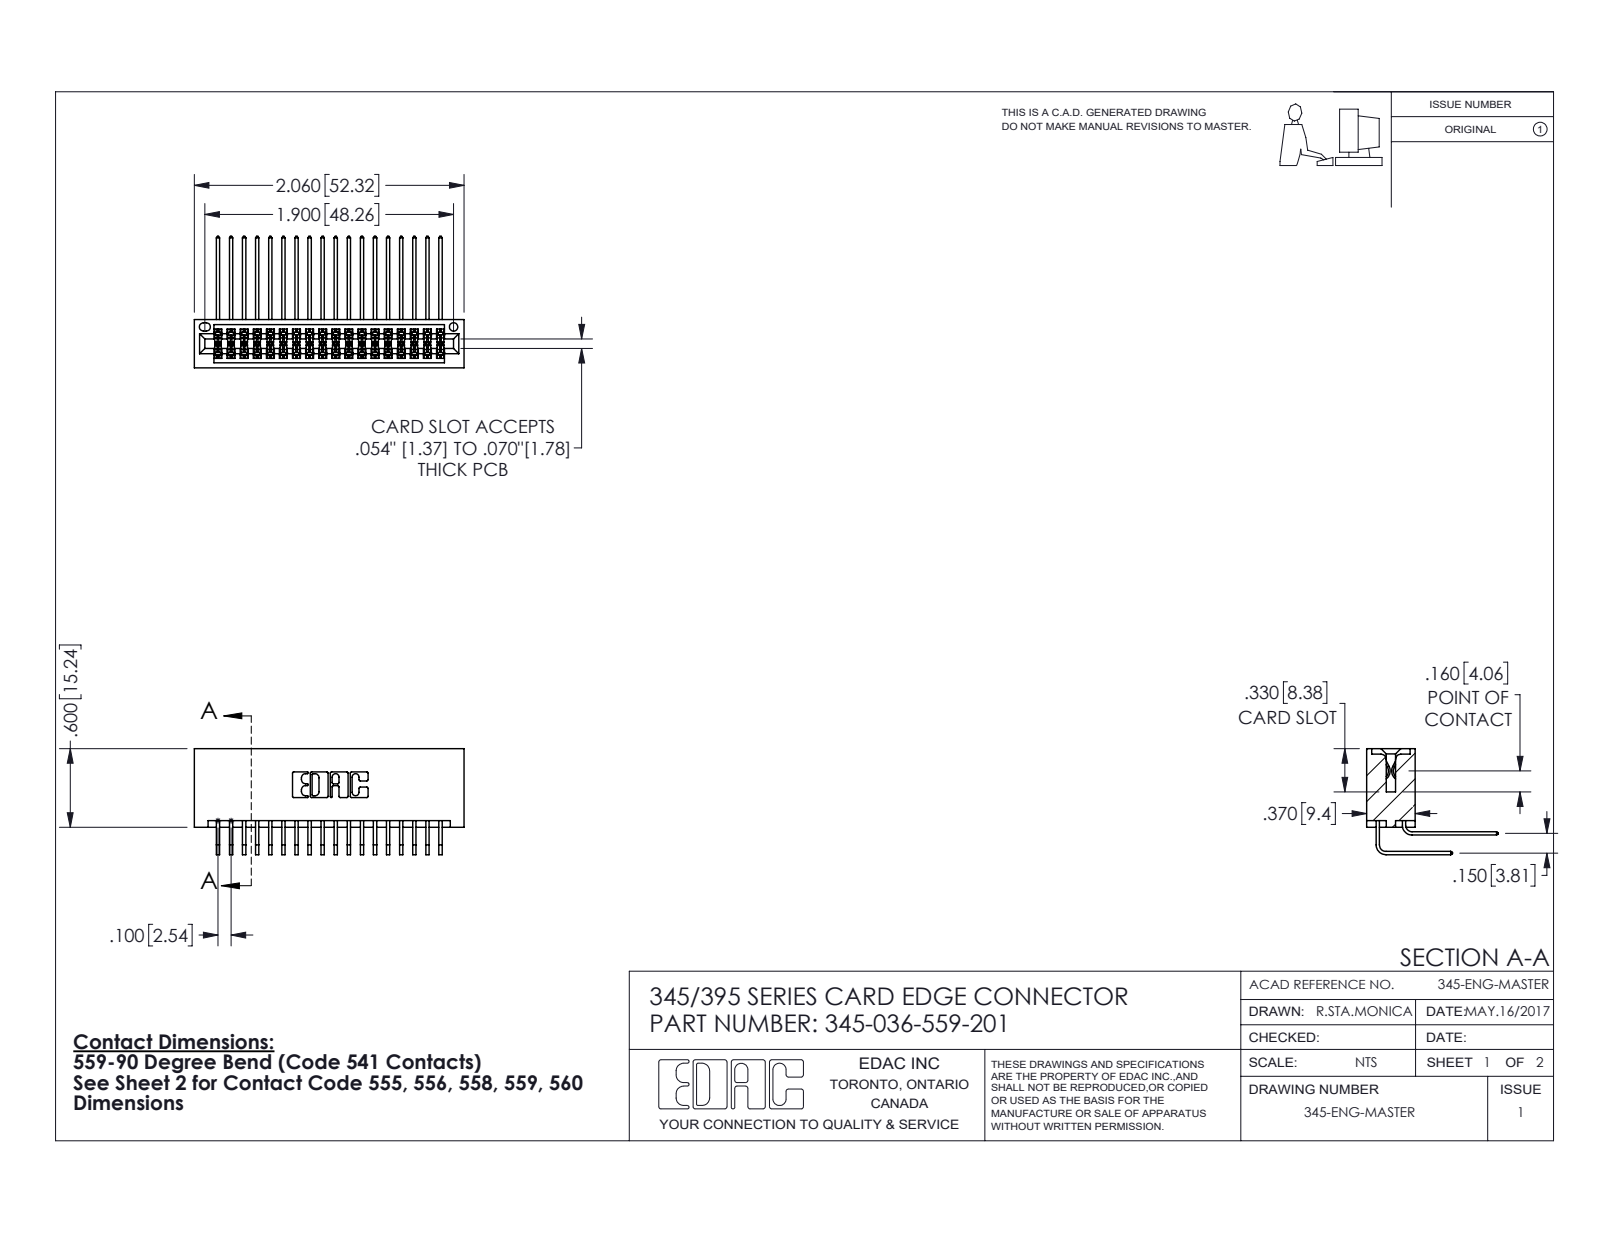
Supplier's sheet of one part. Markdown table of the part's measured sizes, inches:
| quantity | value |
| --- | --- |
| part name | 345-292-001_559 Tail - 2; 345 Part_No Mounting Lugs; 345-036-559-201; 345-292-001_558 559 Tail - 1 |
| STEP written by | SolidWorks 2016 (CONFIG_CONTROL_DESIGN) |
| units | inches |
| bodies | 37 solids, 1990 faces (1336 planar, 654 cylindrical, 0 other) |
| overall size | 2.06 × 1.005 × 0.809 |
| volume | 0.347 in³ |
| surface area | 14.29 in² |
| round holes (diameter × count) | 0.064 × 1 |
| partial cylindrical surfaces (radius × count) | 0.006 × 72, 0.01 × 22, 0.007 × 6, 0.031 × 6, 0.026 × 3, 0.014 × 2, 0.019 × 2, 0.022 × 2 |
| main face-to-face distances | 0.072, 0.298, 0.2, 0.37, 0.098, 0.272, 0.025, 0.225, 0.15, 0.175 |
